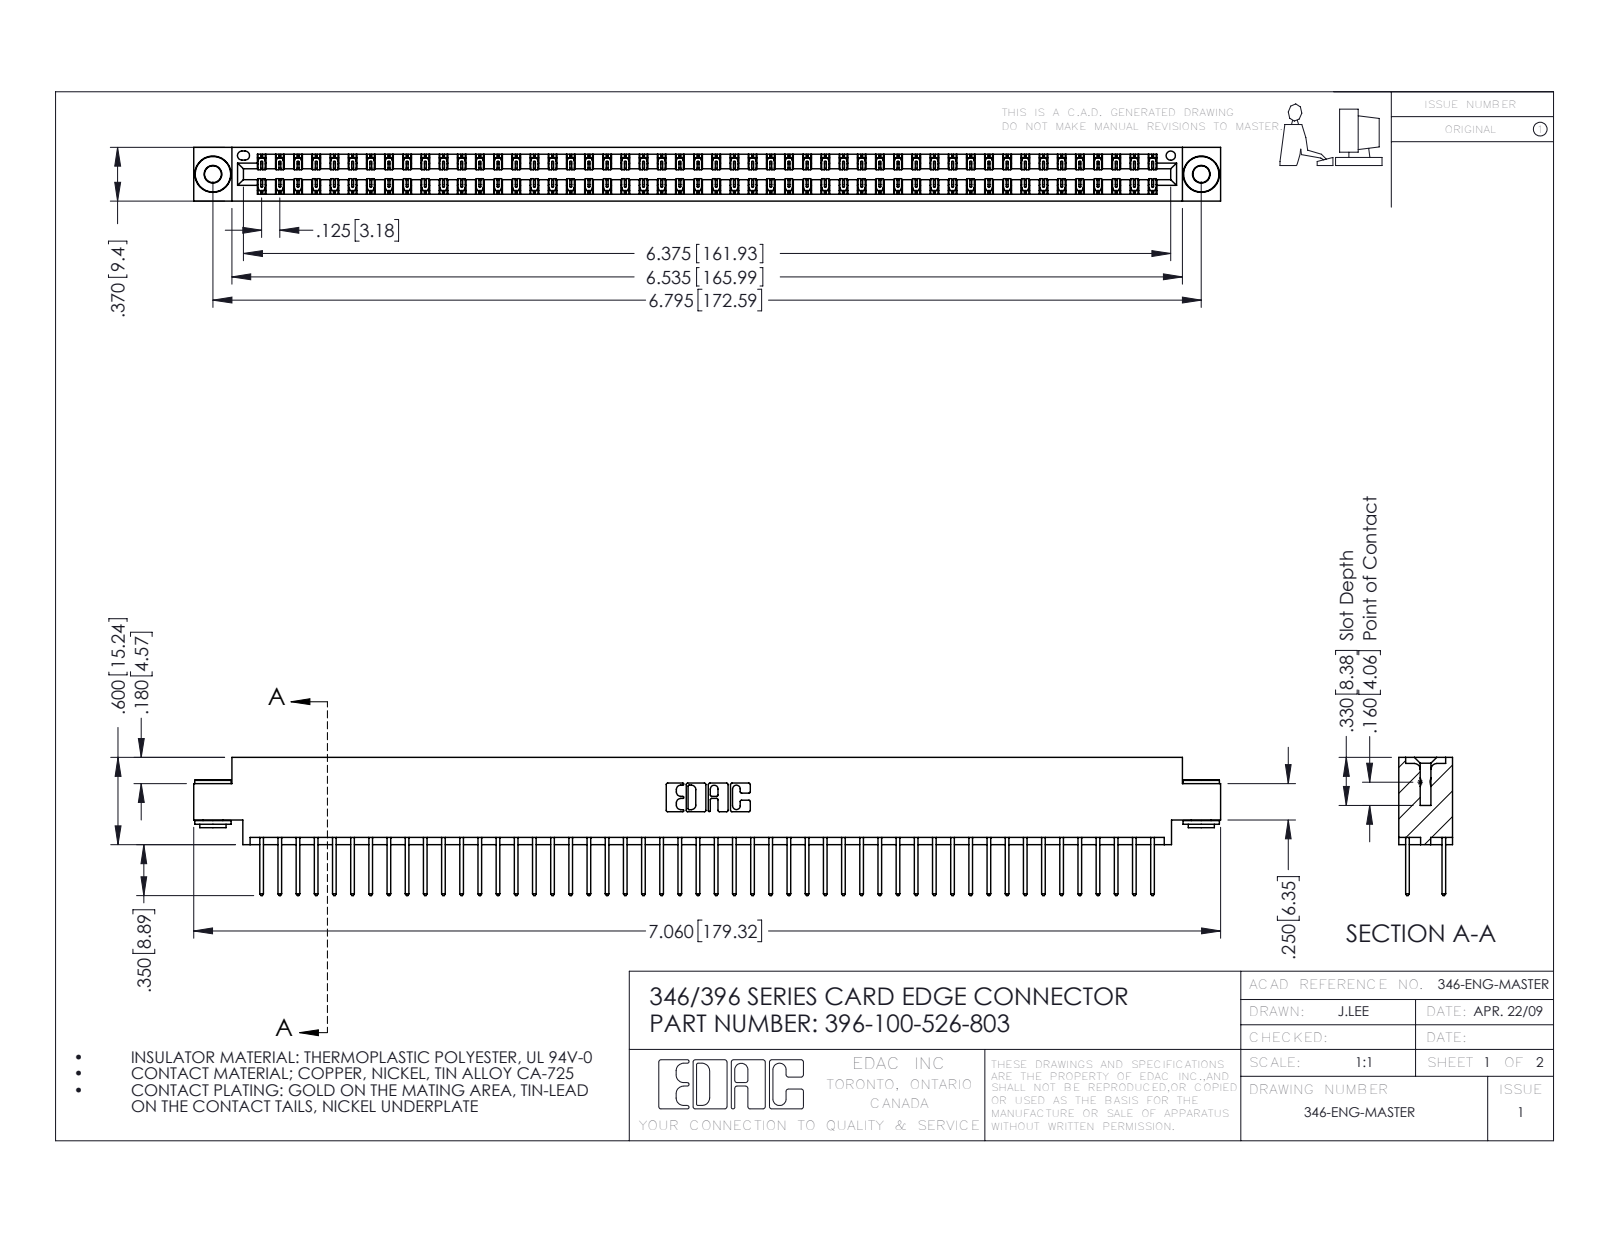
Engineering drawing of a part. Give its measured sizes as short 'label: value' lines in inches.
name: 346 Part_0.170 Offset - 0.156 Dia-TH; 345-250-002_345-250-002-102; 345-292-001_345-293-126; 396-100-526-803
written by: SolidWorks 2016 (CONFIG_CONTROL_DESIGN)
unit: in
bodies: 103 solids, 5364 faces (3590 planar, 1766 cylindrical, 8 other)
size: 7.06 × 0.95 × 0.37
volume: 1.073 in³; area: 39.39 in²
holes: 2× ⌀0.116, 2× ⌀0.156, 1× ⌀0.064
bosses: 2× ⌀0.25, 2× ⌀0.18, 2× ⌀0.136
rounds: 150× R0.006, 100× R0.01, 22× R0.01, 6× R0.007, 6× R0.031, 3× R0.026, 2× R0.014, 2× R0.022
face distances: 0.048, 0.322, 0.25, 0.37, 0.025, 0.072, 0.298, 0.275, 0.148, 0.222
hole spacings: 0.246, 6.586, 6.795
